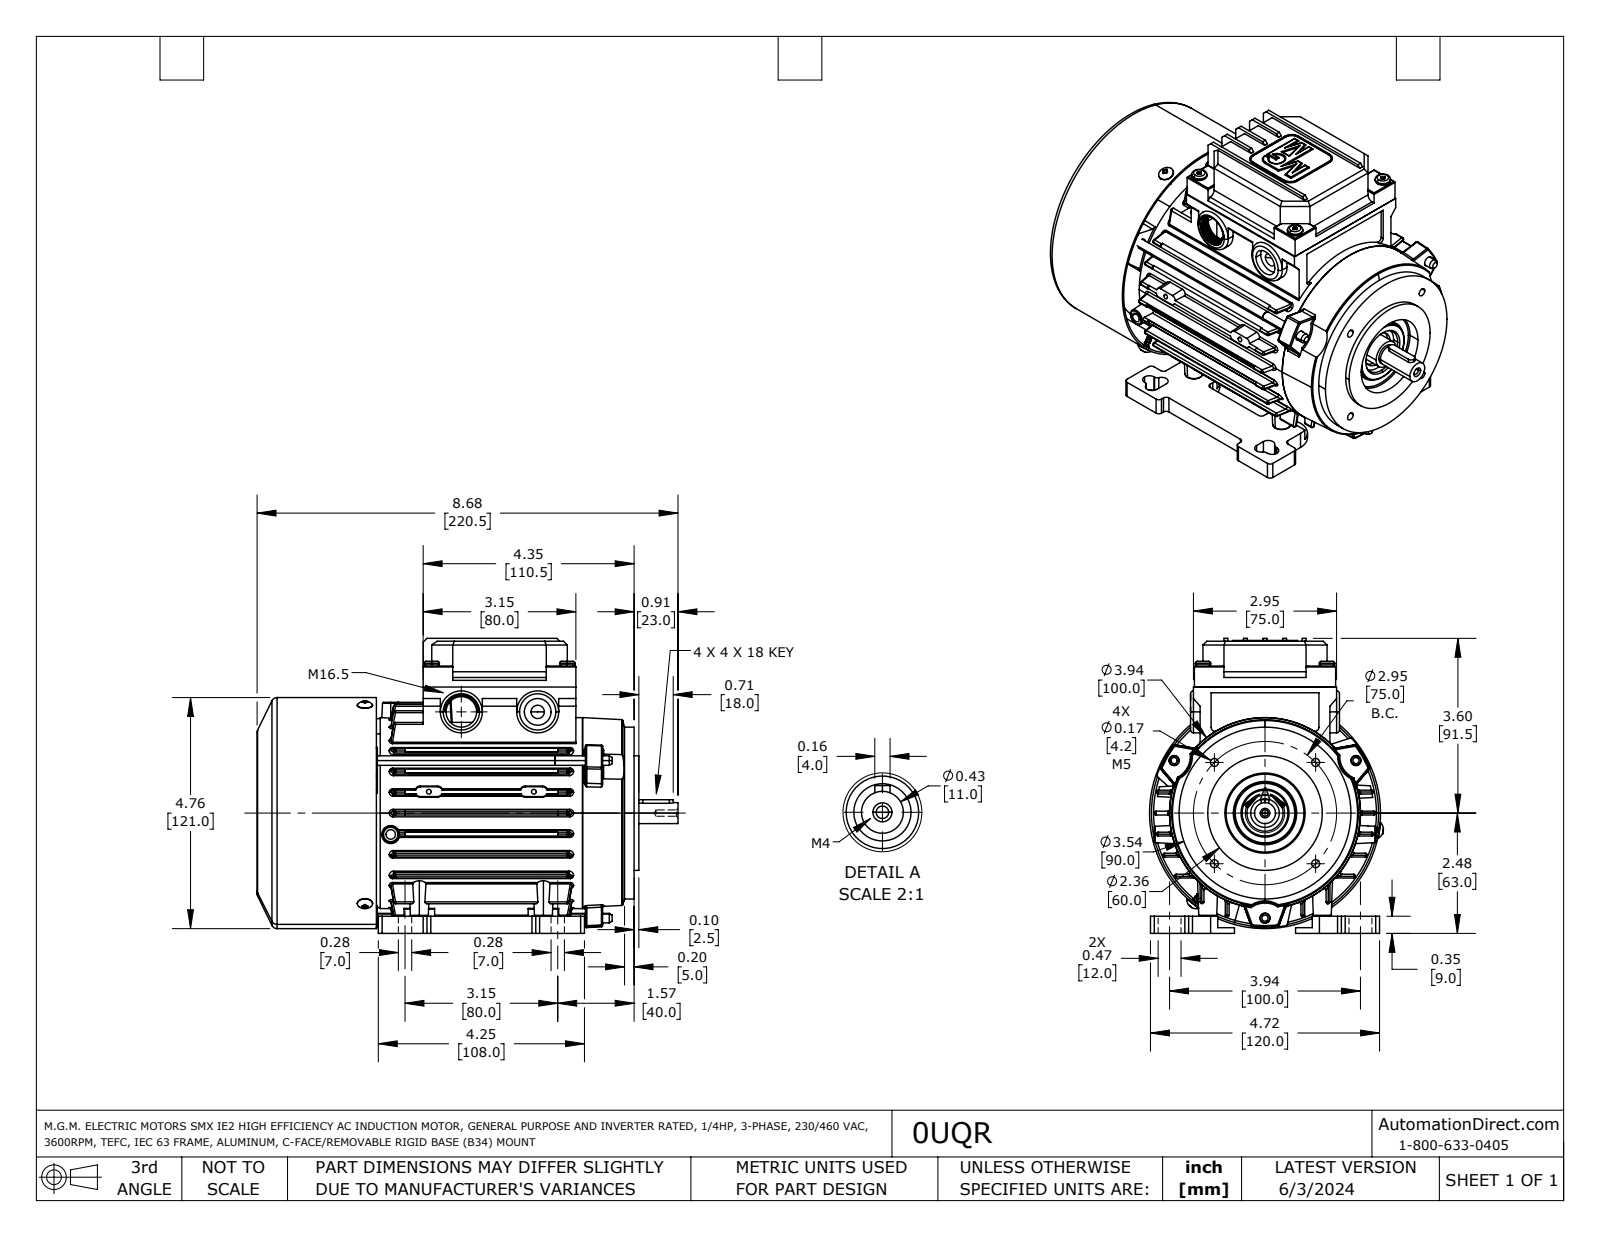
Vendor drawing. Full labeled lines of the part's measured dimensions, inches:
Part name (STEP PRODUCT): 0UQR
STEP written by: SolidWorks 2021 (AUTOMOTIVE_DESIGN)
Units: inches
Bodies: 26 solids, 3576 faces (1148 planar, 1324 cylindrical, 1104 other)
Overall size (bounding box): 8.681 × 6.083 × 4.824
Volume: 31.8 in³ · Surface area: 499.7 in²
Round holes (diameter × count): ⌀0.13 ×8, ⌀0.157 ×7, ⌀0.217 ×7, ⌀0.165 ×4, ⌀0.256 ×4, ⌀0.394 ×4, ⌀0.126 ×3, ⌀0.276 ×3, ⌀0.098 ×2, ⌀0.197 ×2, ⌀0.63 ×2, ⌀0.315 ×1
Round bosses / shafts (diameter × count): ⌀0.118 ×10, ⌀0.315 ×7, ⌀0.197 ×7, ⌀0.386 ×4, ⌀0.138 ×4, ⌀0.079 ×3, ⌀4.764 ×1, ⌀3.937 ×1
Partial cylindrical surfaces — rounded edges, fillets, slot ends (radius × count): R0.039 ×281, R0.008 ×56, R0.016 ×36, R0.02 ×36, R0.079 ×36, R0.004 ×16, R0.033 ×16, R0.014 ×12
Main face-to-face distances: 0.079, 0.866, 0.433, 0.354, 1.299, 0.945, 1.732, 0.787, 0.512, 0.059
Hole centre spacings: 3.717, 1.476, 2.088, 2.165, 2.559, 2.126, 3.75, 0.039
